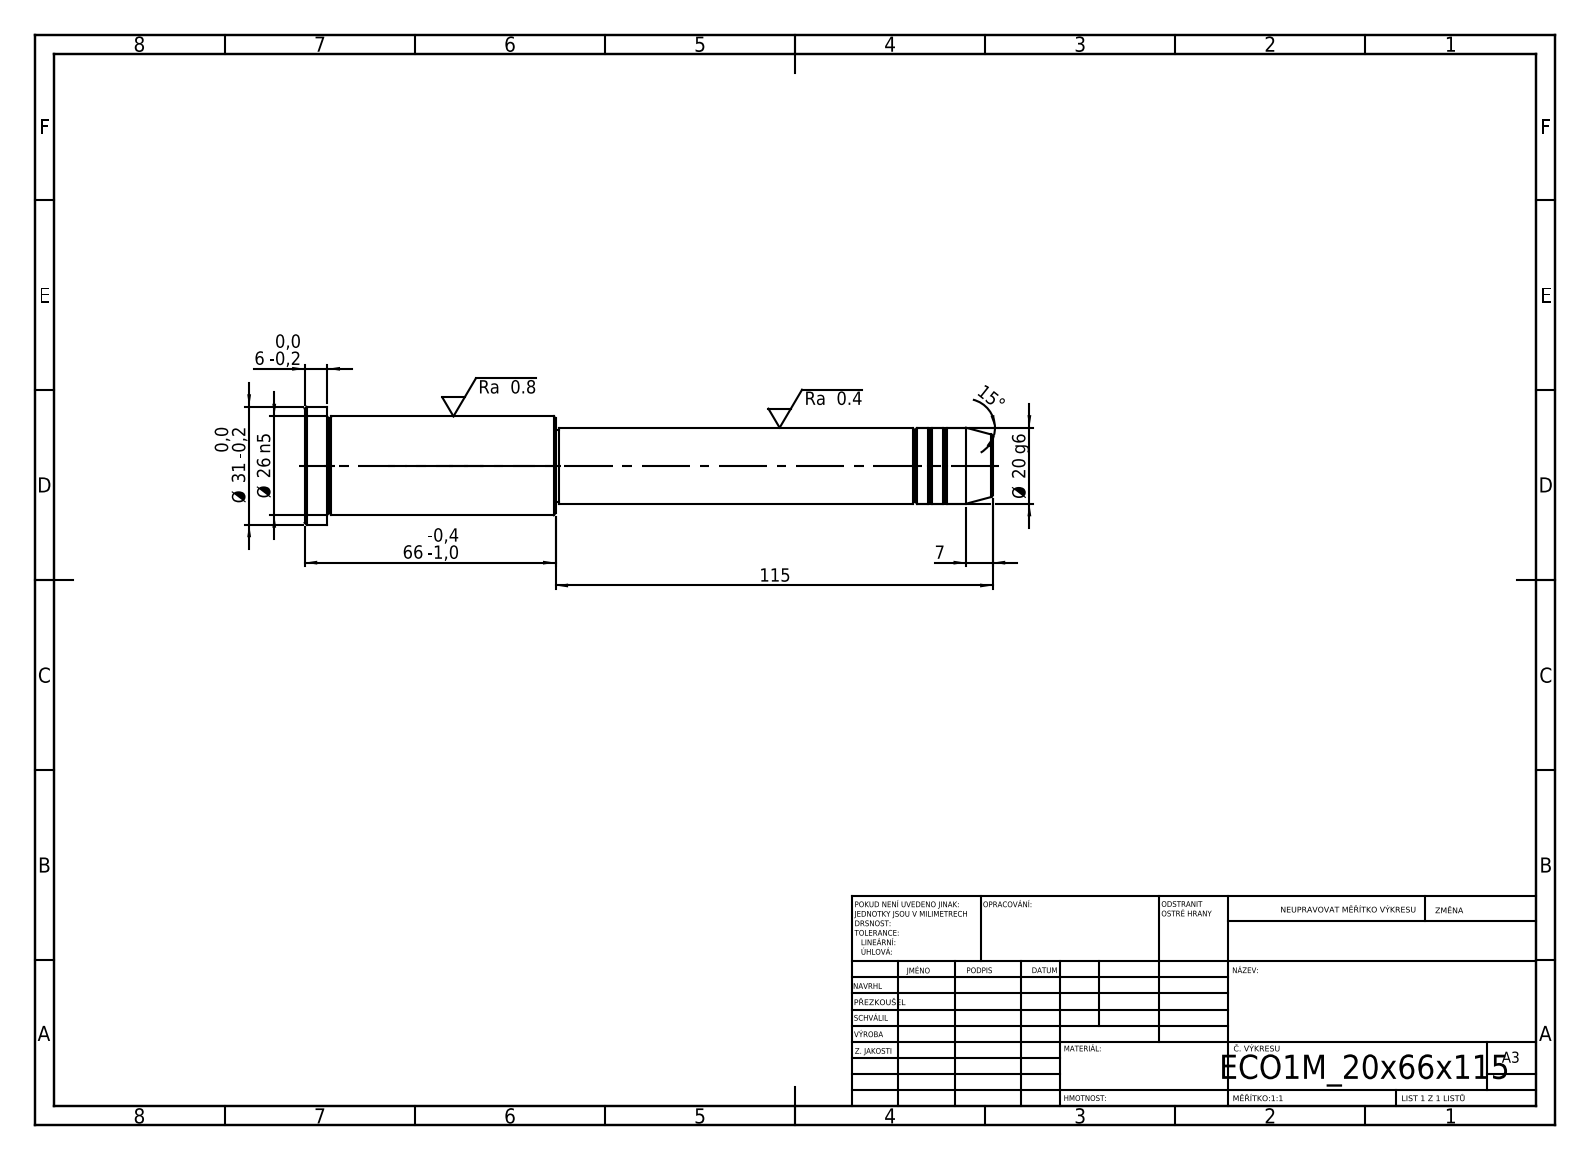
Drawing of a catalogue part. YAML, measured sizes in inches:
step_written_by: "SolidWorks 2019 (CONFIG_CONTROL_DESIGN)"
units: inches
bodies: {solids: 1, faces: 43, planar: 5, cylindrical: 14, other: 24}
overall_size: [7.126, 1.22, 1.22]
volume: 4.392
surface_area: 22.05
round_bosses_or_shafts:
  - {diameter: 1.22, count: 1}
  - {diameter: 1.024, count: 1}
  - {diameter: 0.787, count: 1}
  - {diameter: 0.748, count: 1}
face_to_face_distances: [0.236, 2.362, 2.598, 4.528, 6.89, 7.126, 4.488, 0.039, 2.402, 2.638]
